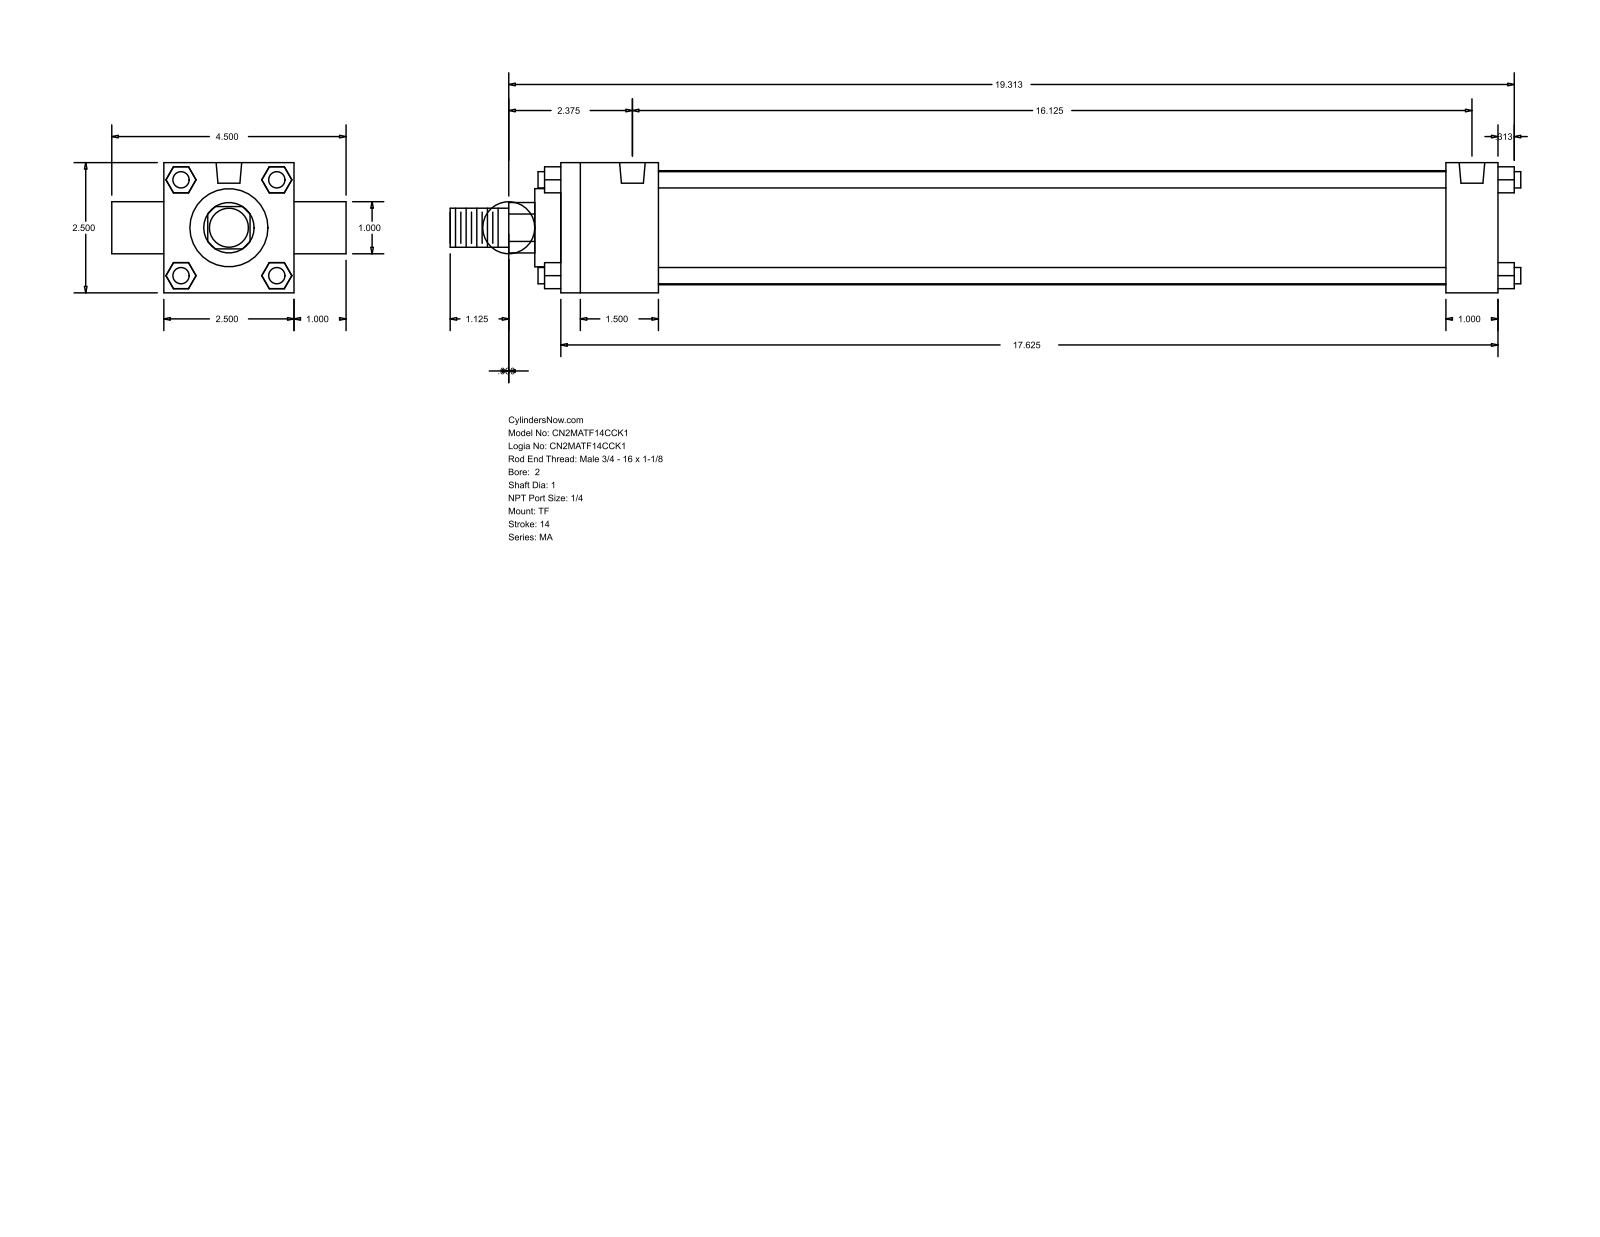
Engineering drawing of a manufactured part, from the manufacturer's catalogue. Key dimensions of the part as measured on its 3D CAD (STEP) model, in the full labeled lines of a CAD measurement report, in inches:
Part name (STEP PRODUCT): MA_TF__0200_1
STEP written by: GSSL Pune (CONFIG_CONTROL_DESIGN)
Units: inches
Bodies: 0 solids, 120 faces (92 planar, 28 cylindrical, 0 other)
Overall size (bounding box): 20.563 × 4.5 × 2.5
Round holes (diameter × count): ⌀0.313 ×3, ⌀0.492 ×2
Round bosses / shafts (diameter × count): ⌀0.313 ×4, ⌀1 ×2, ⌀2.19 ×1, ⌀1.5 ×1, ⌀0.75 ×1
Partial cylindrical surfaces — rounded edges, fillets, slot ends (radius × count): R0.484 ×1
Main face-to-face distances: 2.5, 1, 18, 0.5, 1.875, 17, 15.125, 16.125, 3.5, 1.593
Hole centre spacings: 16.125
